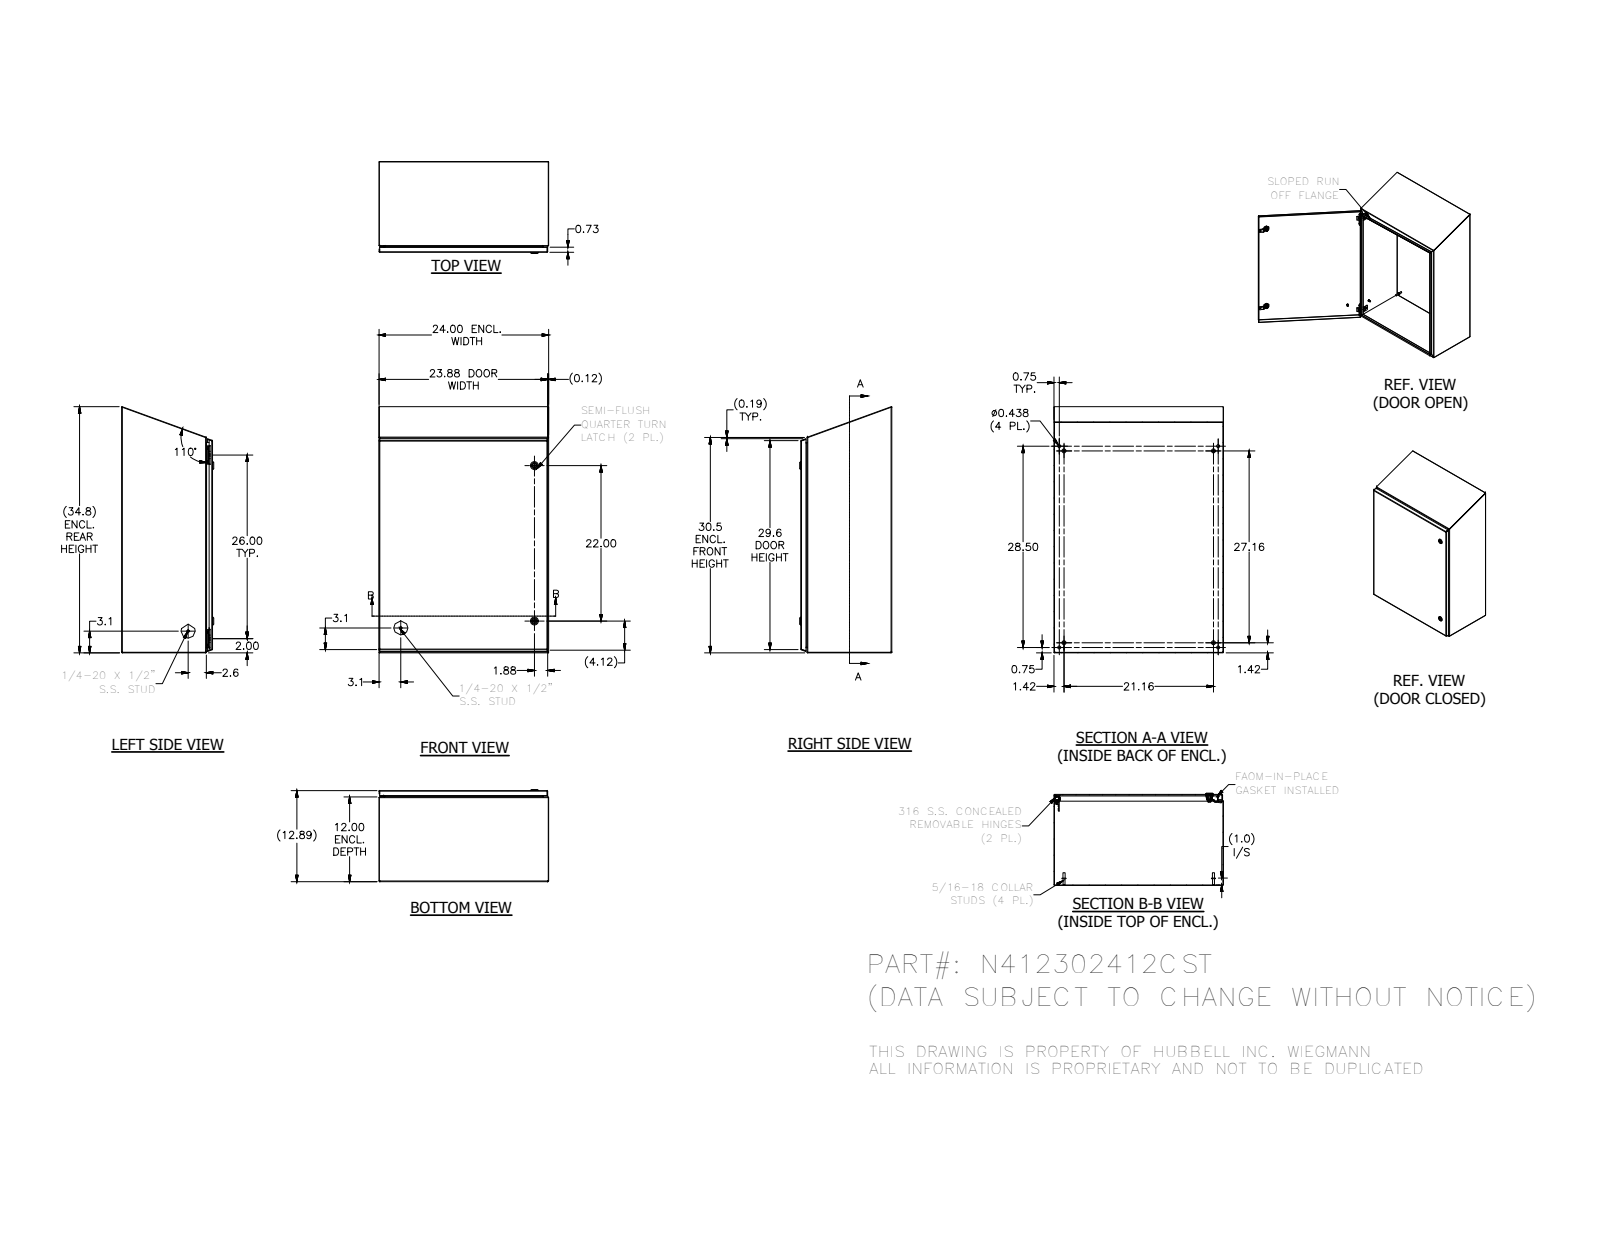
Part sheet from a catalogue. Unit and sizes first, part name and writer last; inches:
Units: inches
Overall size (bounding box): 34.847 × 24 × 13.044
Round holes (diameter × count): ⌀0.093 ×4, ⌀0.152 ×4, ⌀0.167 ×4, ⌀0.172 ×4, ⌀0.187 ×4, ⌀0.437 ×4, ⌀0.156 ×3, ⌀0.197 ×2, ⌀0.315 ×2, ⌀0.394 ×2, ⌀0.402 ×2, ⌀0.634 ×2
Round bosses / shafts (diameter × count): ⌀0.25 ×10, ⌀0.563 ×4, ⌀0.36 ×4, ⌀0.32 ×4, ⌀0.3 ×4, ⌀0.275 ×4, ⌀0.256 ×4, ⌀0.164 ×4
Partial cylindrical surfaces — rounded edges, fillets, slot ends (radius × count): R0.012 ×54, R0.031 ×29, R0.05 ×26, R0.02 ×23, R0.105 ×19, R0.016 ×18, R0.125 ×16, R0.032 ×8
Main face-to-face distances: 0.074, 12.813, 23.926, 12.887, 12.739, 23.852, 24, 11.926, 0.887, 0.813
Hole centre spacings: 26, 22.869, 0.5, 0.656, 0.66, 0.984, 1.307, 1.311
Volume: 233.4 in³ · Surface area: 6 365 in²
Bodies: 40 solids, 1934 faces (775 planar, 694 cylindrical, 465 other)
Part name (STEP PRODUCT): N412_CST-assm; N412302412CSTB3S; HFW3161; HFW328176 (+8 more)
STEP written by: Autodesk Inventor 2012 (AUTOMOTIVE_DESIGN)
